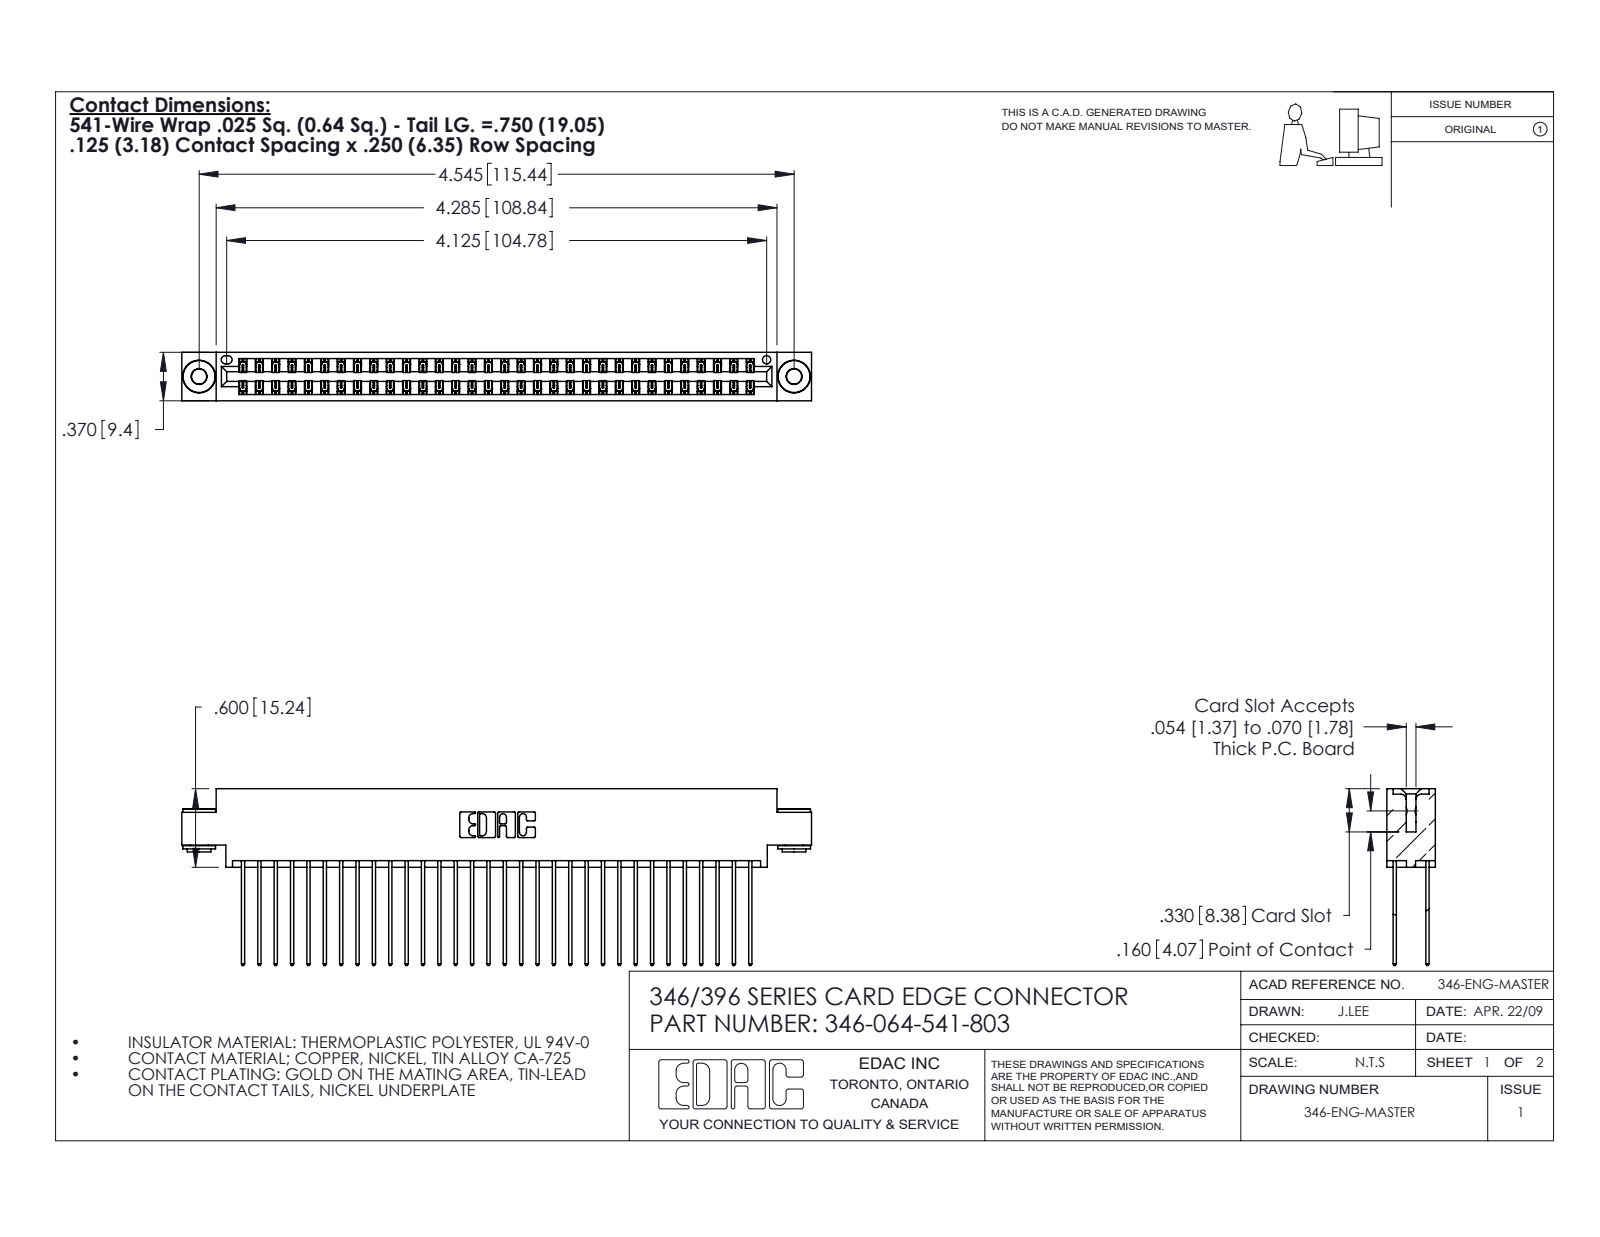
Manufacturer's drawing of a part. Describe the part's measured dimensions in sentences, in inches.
The part is named "345-250-002_345-250-002-102; 346-064-541-803; 346 Part_0.170 Offset - 0.156 Dia-TH; 345-292-001_345-293-141". Its 3-D file was written by "SolidWorks 2020 (CONFIG_CONTROL_DESIGN)". It is 67 solids with 3506 faces: 2344 planar, 1154 cylindrical and 8 other. Overall it measures 4.81 by 1.35 by 0.37 inches. Its volume is 0.735 cubic inches and its surface area 28.82 square inches. Round holes: 2 of diameter 0.116, 2 of diameter 0.156, 1 of diameter 0.064. Round bosses or shafts: 2 of diameter 0.25, 2 of diameter 0.18, 2 of diameter 0.136. Partial cylindrical surfaces (rounded edges, fillets, slot ends): 96 of radius 0.006, 64 of radius 0.01, 22 of radius 0.01, 6 of radius 0.007, 6 of radius 0.031, 3 of radius 0.026, 2 of radius 0.014, 2 of radius 0.022. The main face-to-face distances are 0.048, 0.322, 0.25, 0.025, 0.072, 0.298, 0.37, 0.275, 0.225, 0.222. The hole center spacings are 0.246, 4.337, 4.545.
